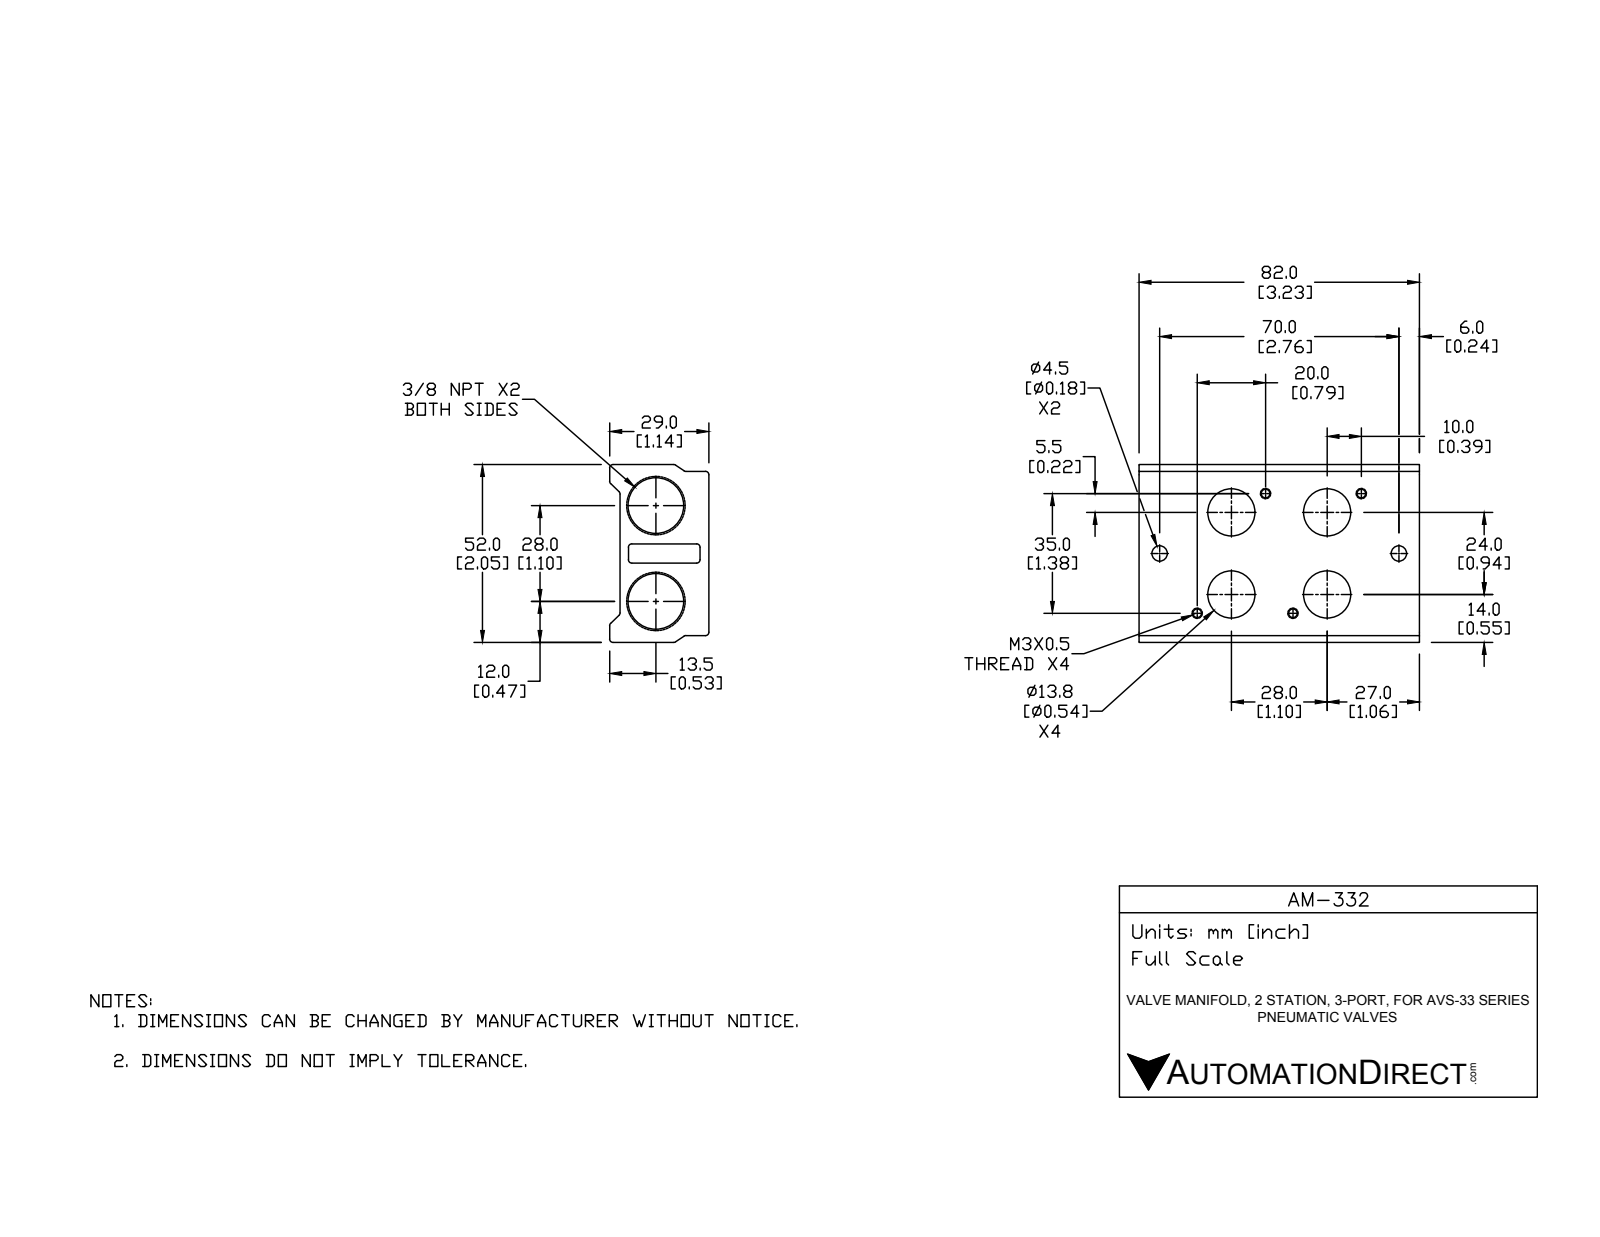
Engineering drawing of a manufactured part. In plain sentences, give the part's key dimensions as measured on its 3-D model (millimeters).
The part is named "AM-332". Its 3-D file was written by "SolidWorks 2016 (AUTOMOTIVE_DESIGN)". It is 1 solid with 126 faces: 26 planar, 60 cylindrical and 40 other. Overall it measures 82 by 52 by 29 millimeters. Its volume is 70 483 cubic millimeters and its surface area 27 239 square millimeters. Round holes: 4 of diameter 2.5, 4 of diameter 13.8, 2 of diameter 4.5, 2 of diameter 11.11, 2 of diameter 14.27. Partial cylindrical surfaces (rounded edges, fillets, slot ends): 16 of radius 1. The main face-to-face distances are 23.2, 28.8, 26, 5.6, 52, 2, 50, 21.2, 26.8, 82. The hole center spacings are 28, 11.41, 24.19, 31.15, 50.45, 18.82, 20.67, 24.
